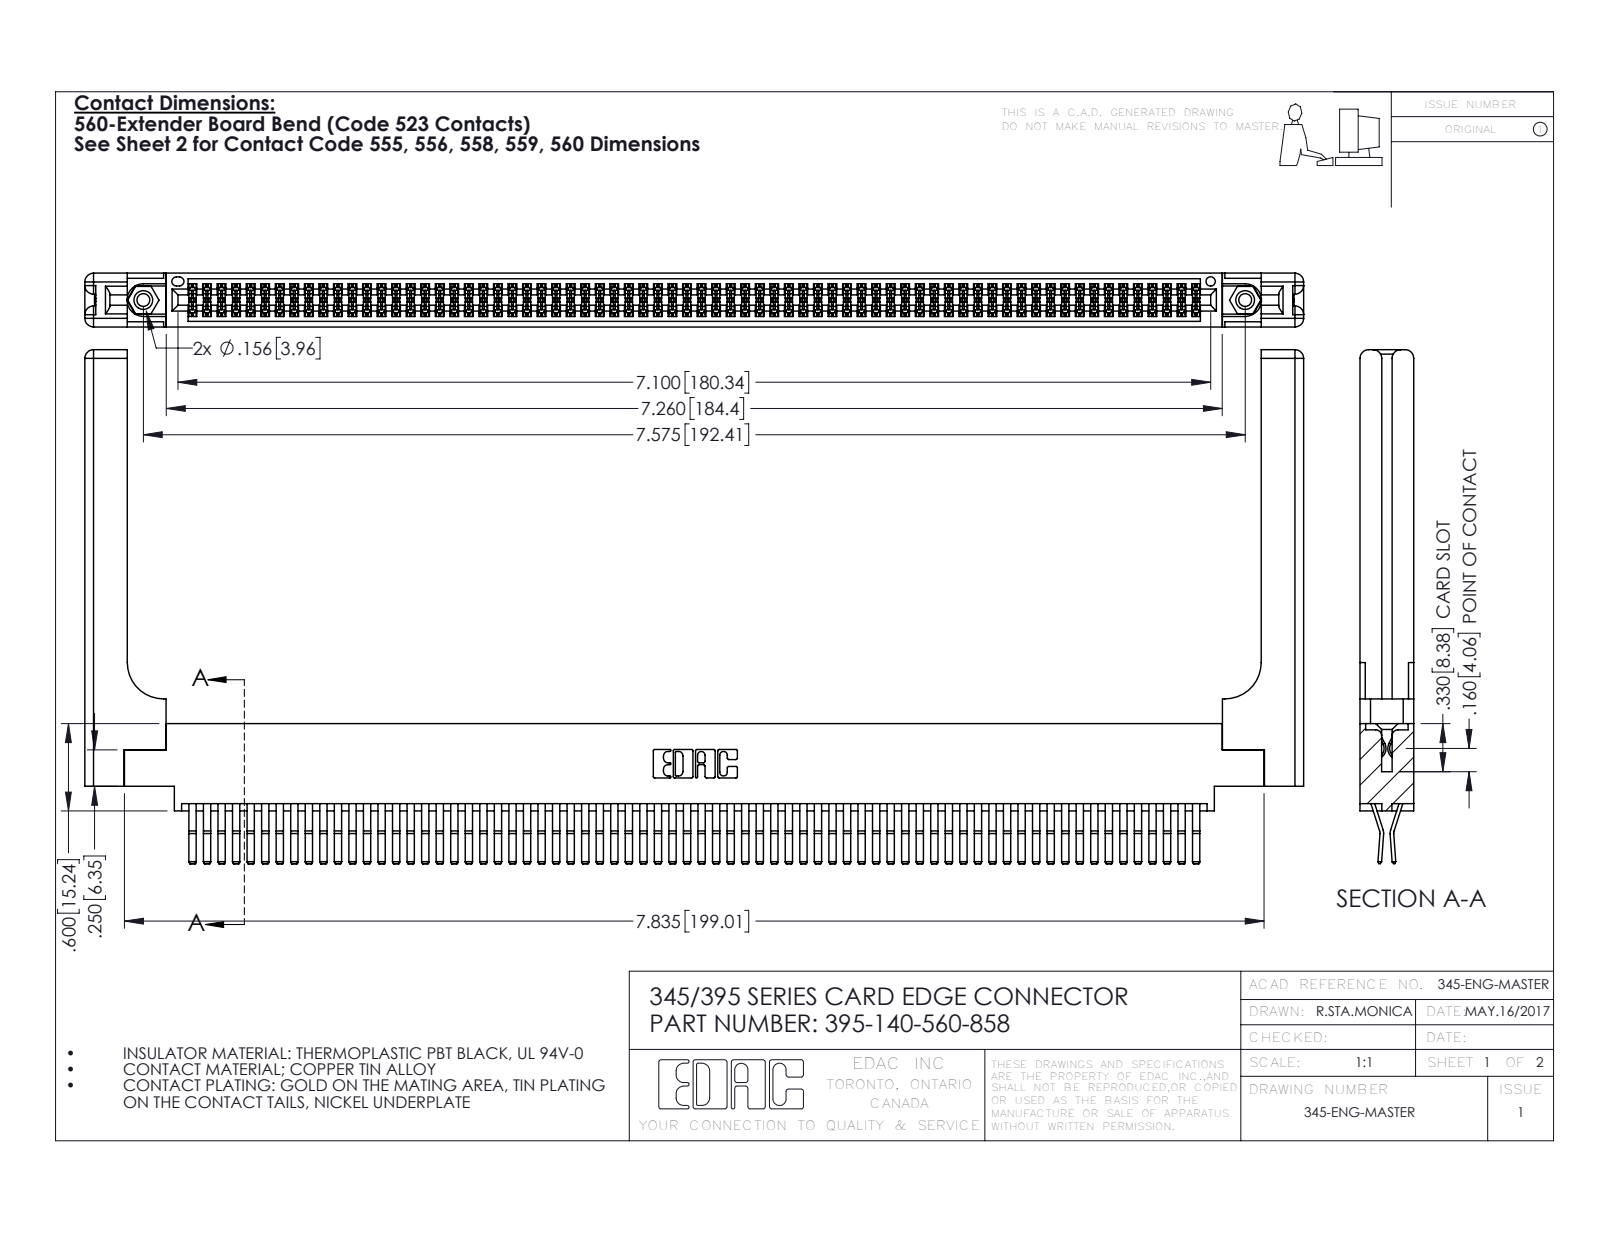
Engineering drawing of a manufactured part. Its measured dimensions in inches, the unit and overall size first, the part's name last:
Units: inches
Overall size (bounding box): 8.379 × 3.532 × 0.37
Round holes (diameter × count): ⌀0.089 ×2, ⌀0.125 ×2, ⌀0.156 ×2, ⌀0.064 ×1
Round bosses / shafts (diameter × count): ⌀0.155 ×2
Partial cylindrical surfaces — rounded edges, fillets, slot ends (radius × count): R0.006 ×210, R0.01 ×22, R0.06 ×16, R0.007 ×6, R0.031 ×6, R0.026 ×3, R0.01 ×2, R0.014 ×2
Main face-to-face distances: 0.072, 0.298, 0.025, 0.37, 0.098, 0.272, 0.2, 0.225, 0.175, 0.148
Hole centre spacings: 0.27, 7.339, 7.575
Volume: 1.844 in³ · Surface area: 62.37 in²
Bodies: 145 solids, 7666 faces (4852 planar, 2754 cylindrical, 60 other)
Part name (STEP PRODUCT): 345 Part_0.170 Offset - 0.156 Dia-TH; 345-220-058_345-220-058; 345-292-001_560 Tail; 395-140-560-858 (+1 more)
STEP written by: SolidWorks 2016 (CONFIG_CONTROL_DESIGN)
